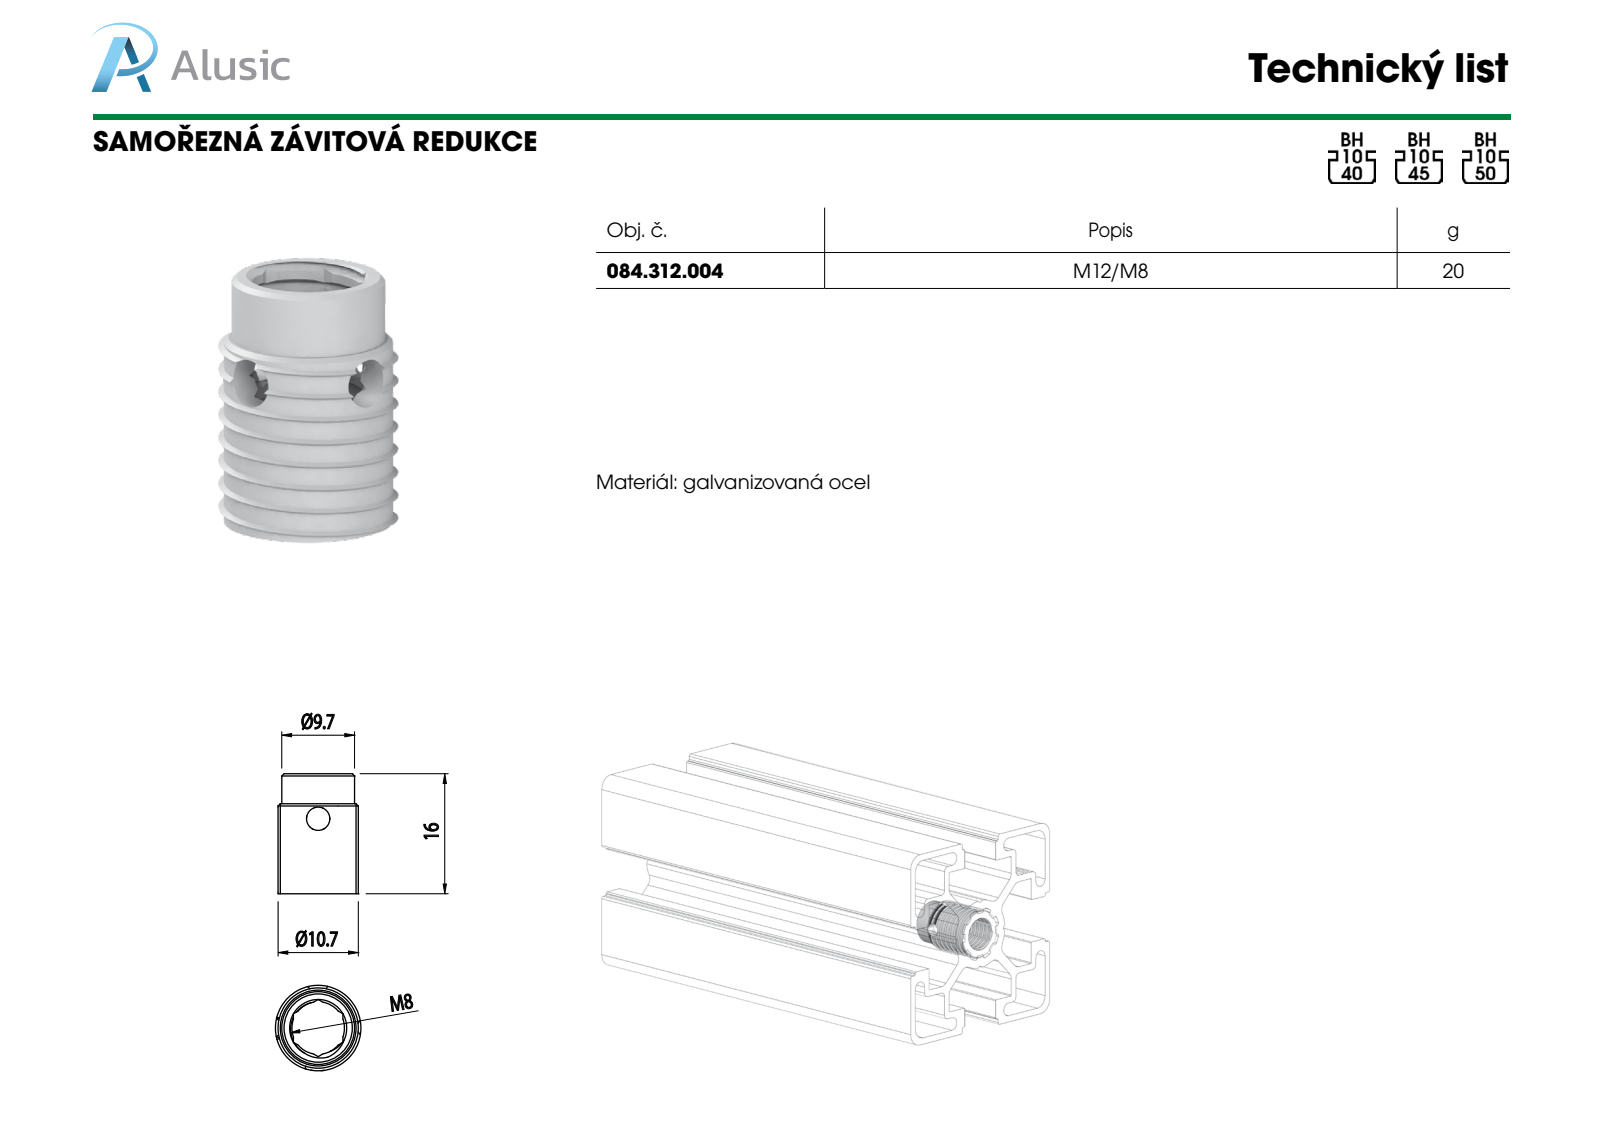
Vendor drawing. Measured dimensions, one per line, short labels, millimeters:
name: 084.312.004
written by: SolidWorks 2011 (CONFIG_CONTROL_DESIGN)
unit: mm
bodies: 1 solid, 332 faces (160 planar, 119 cylindrical, 53 other)
size: 16 × 11.39 × 11.39
volume: 652 mm³; area: 1 267 mm²
holes: 2× ⌀3.1
bosses: 1× ⌀10.7, 1× ⌀9.7
rounds: 1× R3.5
face distances: 6.6, 16, 12, 4
